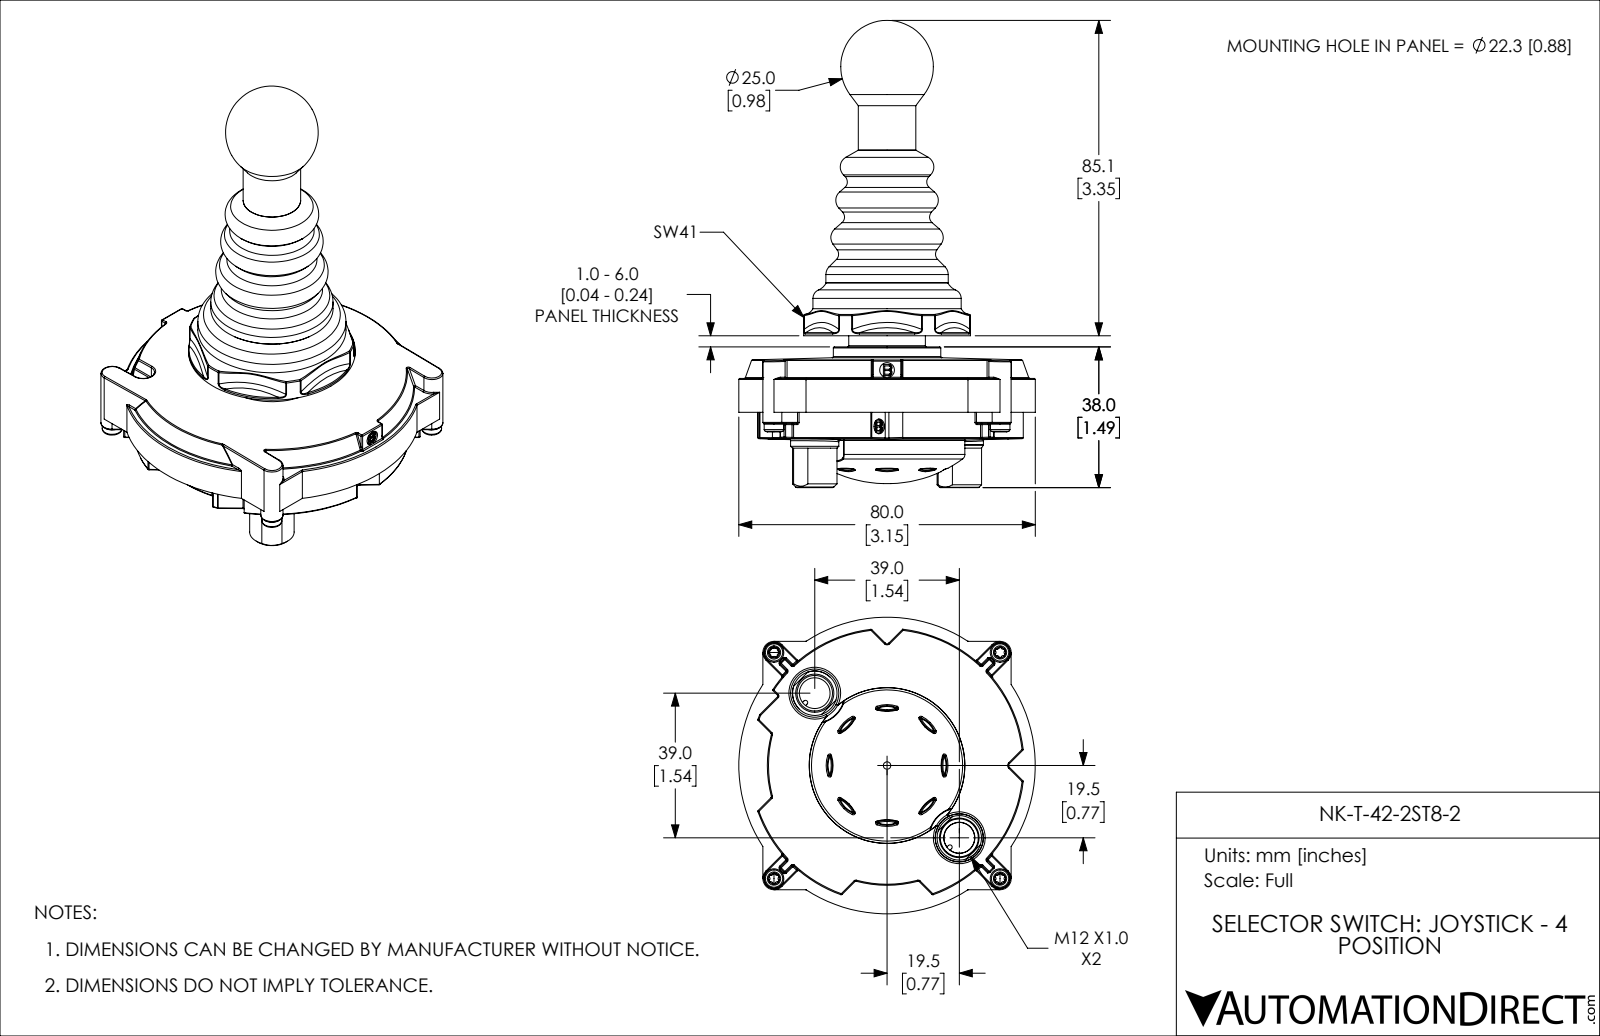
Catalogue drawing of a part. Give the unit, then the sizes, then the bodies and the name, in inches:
Units: inches
Overall size (bounding box): 4.961 × 3.15 × 3.15
Round holes (diameter × count): ⌀0.157 ×5, ⌀0.115 ×4, ⌀0.327 ×2, ⌀0.331 ×1, ⌀1.228 ×1, ⌀1.461 ×1, ⌀1.579 ×1
Round bosses / shafts (diameter × count): ⌀0.209 ×4, ⌀0.512 ×2, ⌀1.772 ×1, ⌀1.654 ×1, ⌀1.575 ×1, ⌀1.303 ×1, ⌀1.299 ×1, ⌀1.142 ×1
Partial cylindrical surfaces — rounded edges, fillets, slot ends (radius × count): R0.012 ×115, R0.007 ×44, R0.02 ×12, R0.024 ×8, R0.102 ×8, R0.354 ×8, R0.118 ×5, R0.027 ×2
Main face-to-face distances: 1.376, 0.555, 0.821, 2.638, 2.784, 1.963, 1.408, 1.016, 0.681, 0.36
Hole centre spacings: 2.402, 1.698, 0.177, 2.016, 2.016, 2.224, 3.396, 0.611
Volume: 10.16 in³ · Surface area: 51.33 in²
Bodies: 4 solids, 1383 faces (383 planar, 350 cylindrical, 650 other)
Part name (STEP PRODUCT): NK-T-42-2ST8-2
STEP written by: SolidWorks 2019 (CONFIG_CONTROL_DESIGN)
